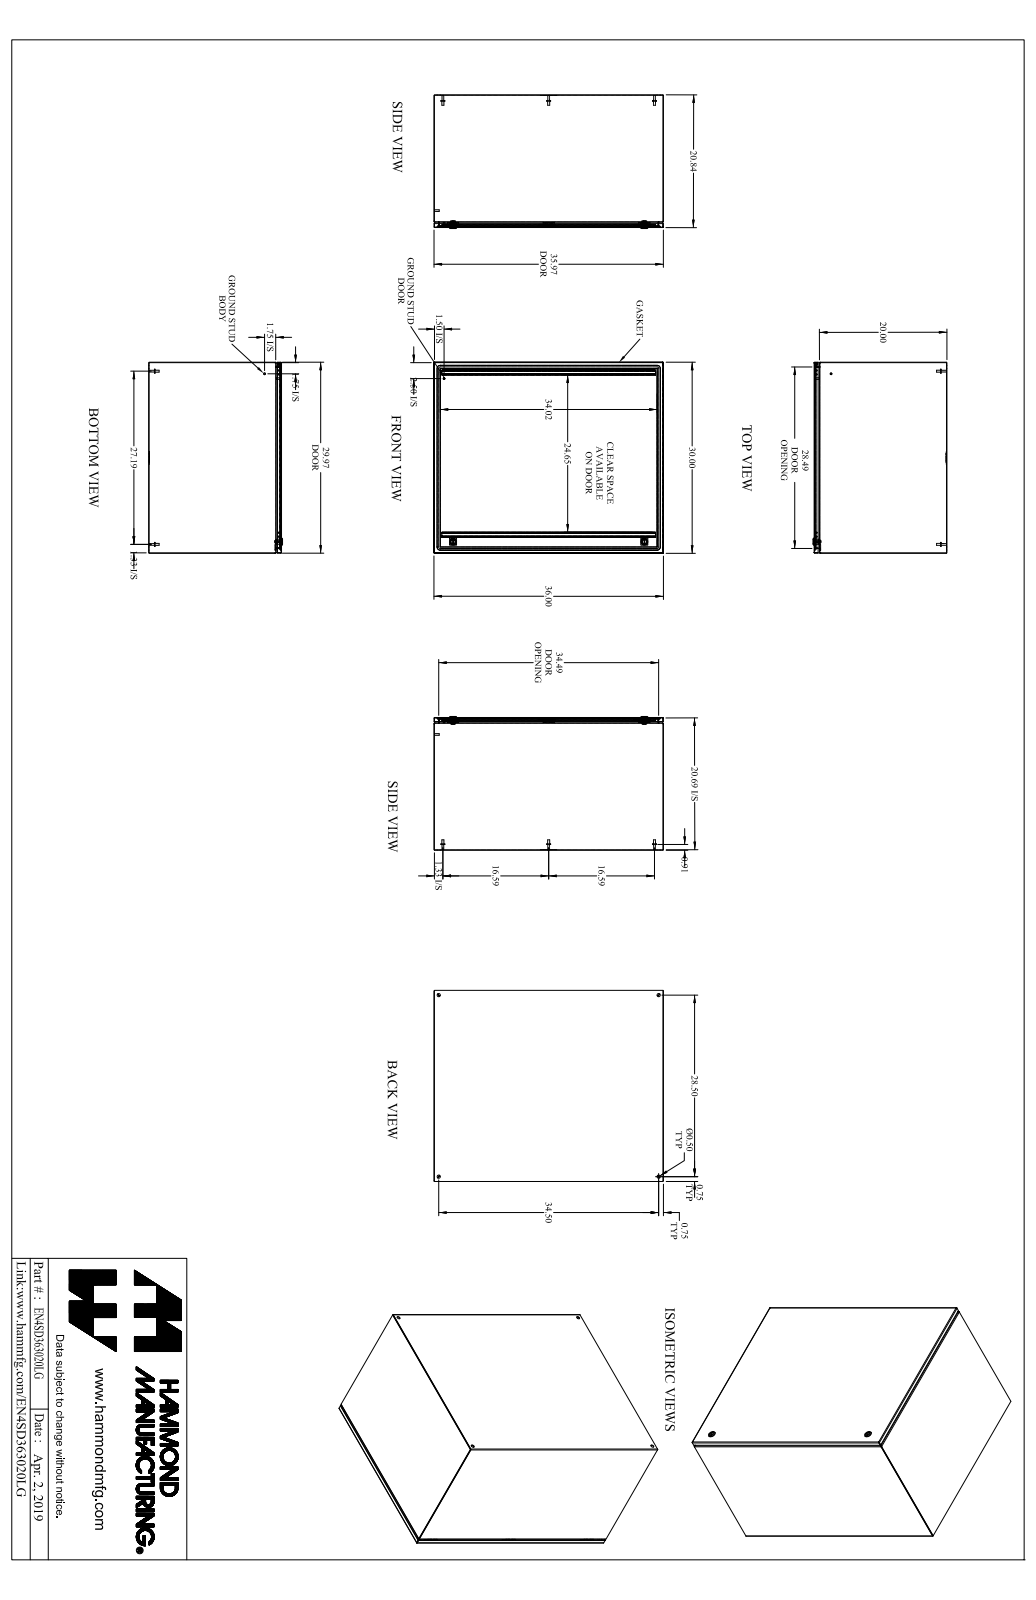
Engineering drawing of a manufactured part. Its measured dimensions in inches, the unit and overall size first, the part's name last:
Units: inches
Overall size (bounding box): 36 × 30 × 20.997
Round holes (diameter × count): ⌀0.5 ×4, ⌀0.232 ×2, ⌀0.625 ×2, ⌀0.785 ×2, ⌀0.172 ×1, ⌀0.24 ×1, ⌀0.242 ×1
Round bosses / shafts (diameter × count): ⌀0.625 ×6, ⌀0.313 ×6, ⌀0.27 ×6, ⌀1.1 ×2, ⌀0.525 ×2, ⌀0.281 ×2, ⌀0.25 ×2, ⌀0.455 ×1
Partial cylindrical surfaces — rounded edges, fillets, slot ends (radius × count): R0.036 ×18, R0.108 ×18, R0.043 ×12, R0.081 ×12, R0.312 ×12, R0.006 ×6, R0.062 ×6, R0.125 ×4
Main face-to-face distances: 0.072, 20.765, 29.928, 35.928, 20.693, 20.837, 29.856, 30, 35.856, 36
Hole centre spacings: 27.519, 28.5, 34.5, 44.749, 2.493, 2.494, 29.999, 32.267
Volume: 381 in³ · Surface area: 10 665 in²
Bodies: 35 solids, 901 faces (434 planar, 295 cylindrical, 172 other)
Part name (STEP PRODUCT): EN4SD363020LG
STEP written by: SolidWorks 2019 (AUTOMOTIVE_DESIGN)
